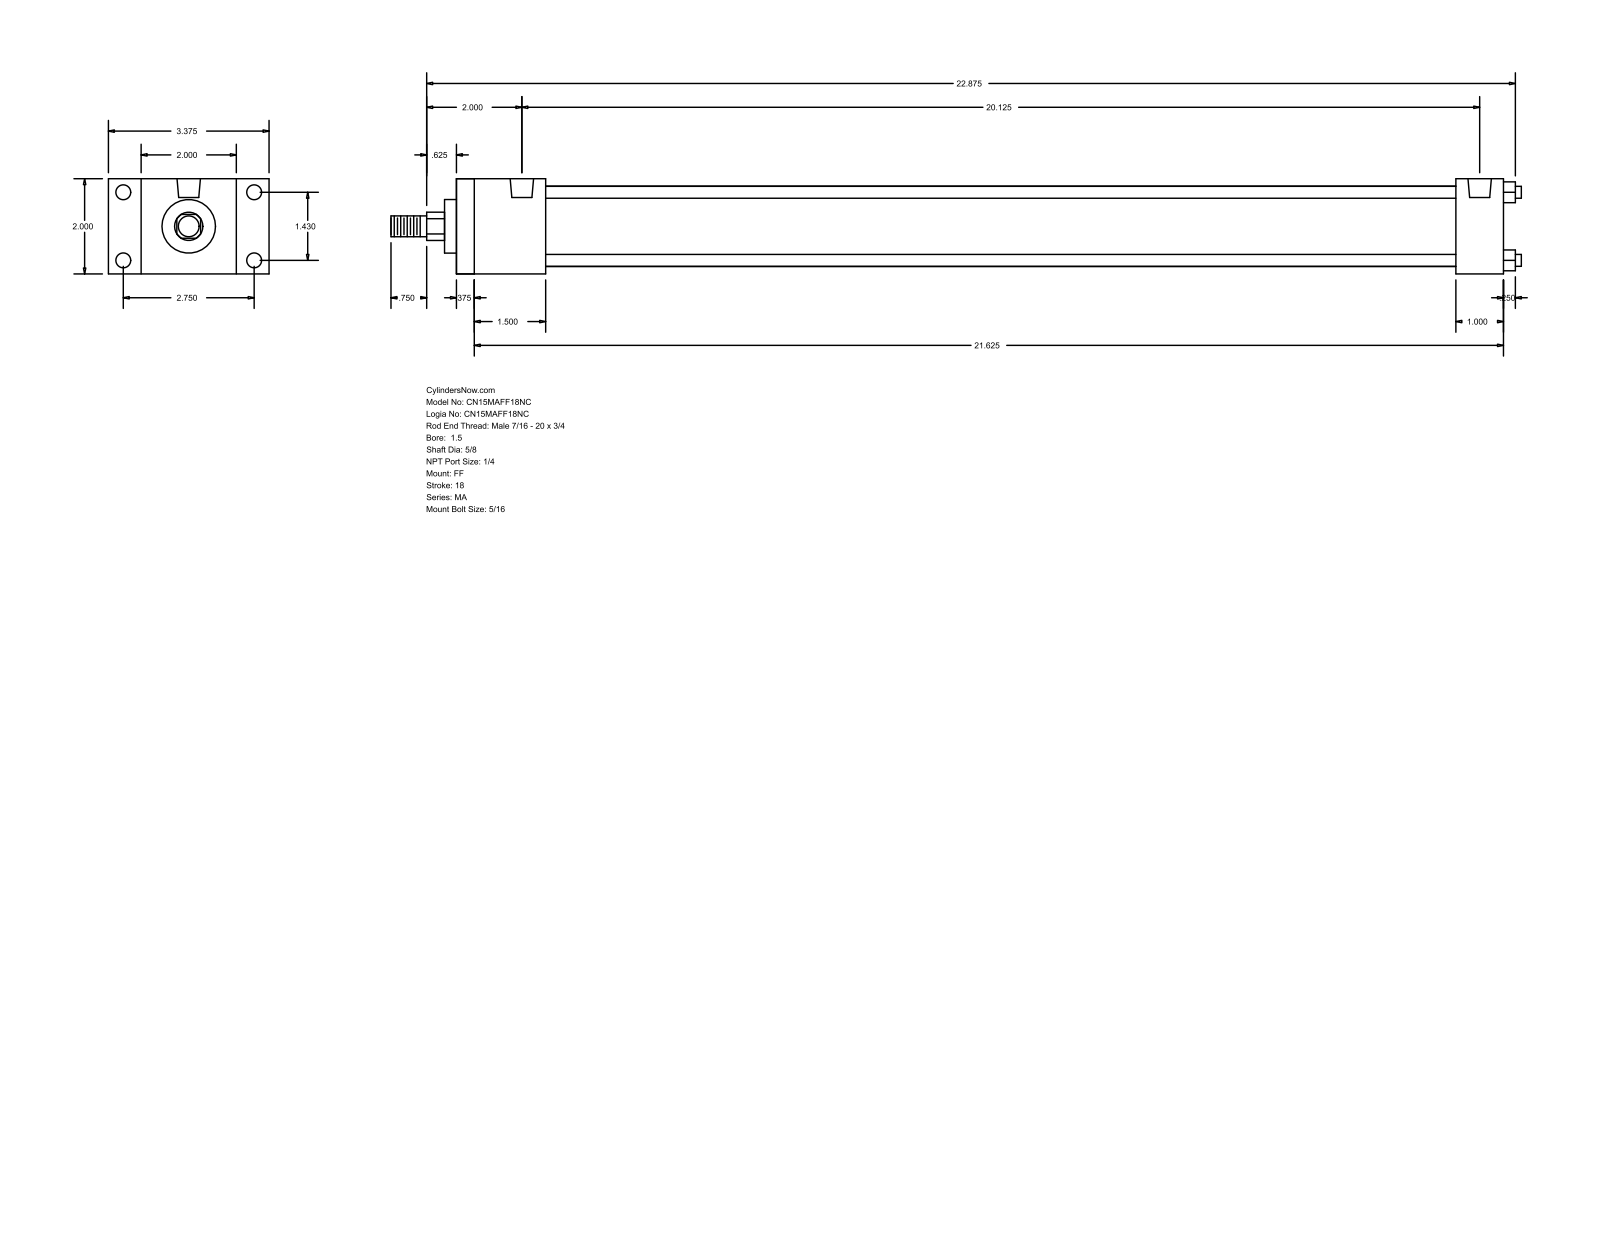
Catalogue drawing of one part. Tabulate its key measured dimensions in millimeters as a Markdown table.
| quantity | value |
| --- | --- |
| part name | MA_FF__0150_0.625 |
| STEP written by | GSSL Pune (CONFIG_CONTROL_DESIGN) |
| units | millimeters |
| bodies | 0 solids, 92 faces (64 planar, 28 cylindrical, 0 other) |
| overall size | 603.25 × 85.72 × 50.8 |
| round holes (diameter × count) | 7.94 × 8, 12.49 × 2 |
| round bosses / shafts (diameter × count) | 6.35 × 4, 42.93 × 1, 28.57 × 1, 15.88 × 1, 11.11 × 1 |
| partial cylindrical surfaces (radius × count) | 7.54 × 1 |
| main face-to-face distances | 50.8, 558.79, 549.27, 9.52, 25.4, 47.62, 533.39, 38.1, 523.87, 485.77 |
| hole center spacings | 36.32, 69.84, 78.72, 511.18 |
